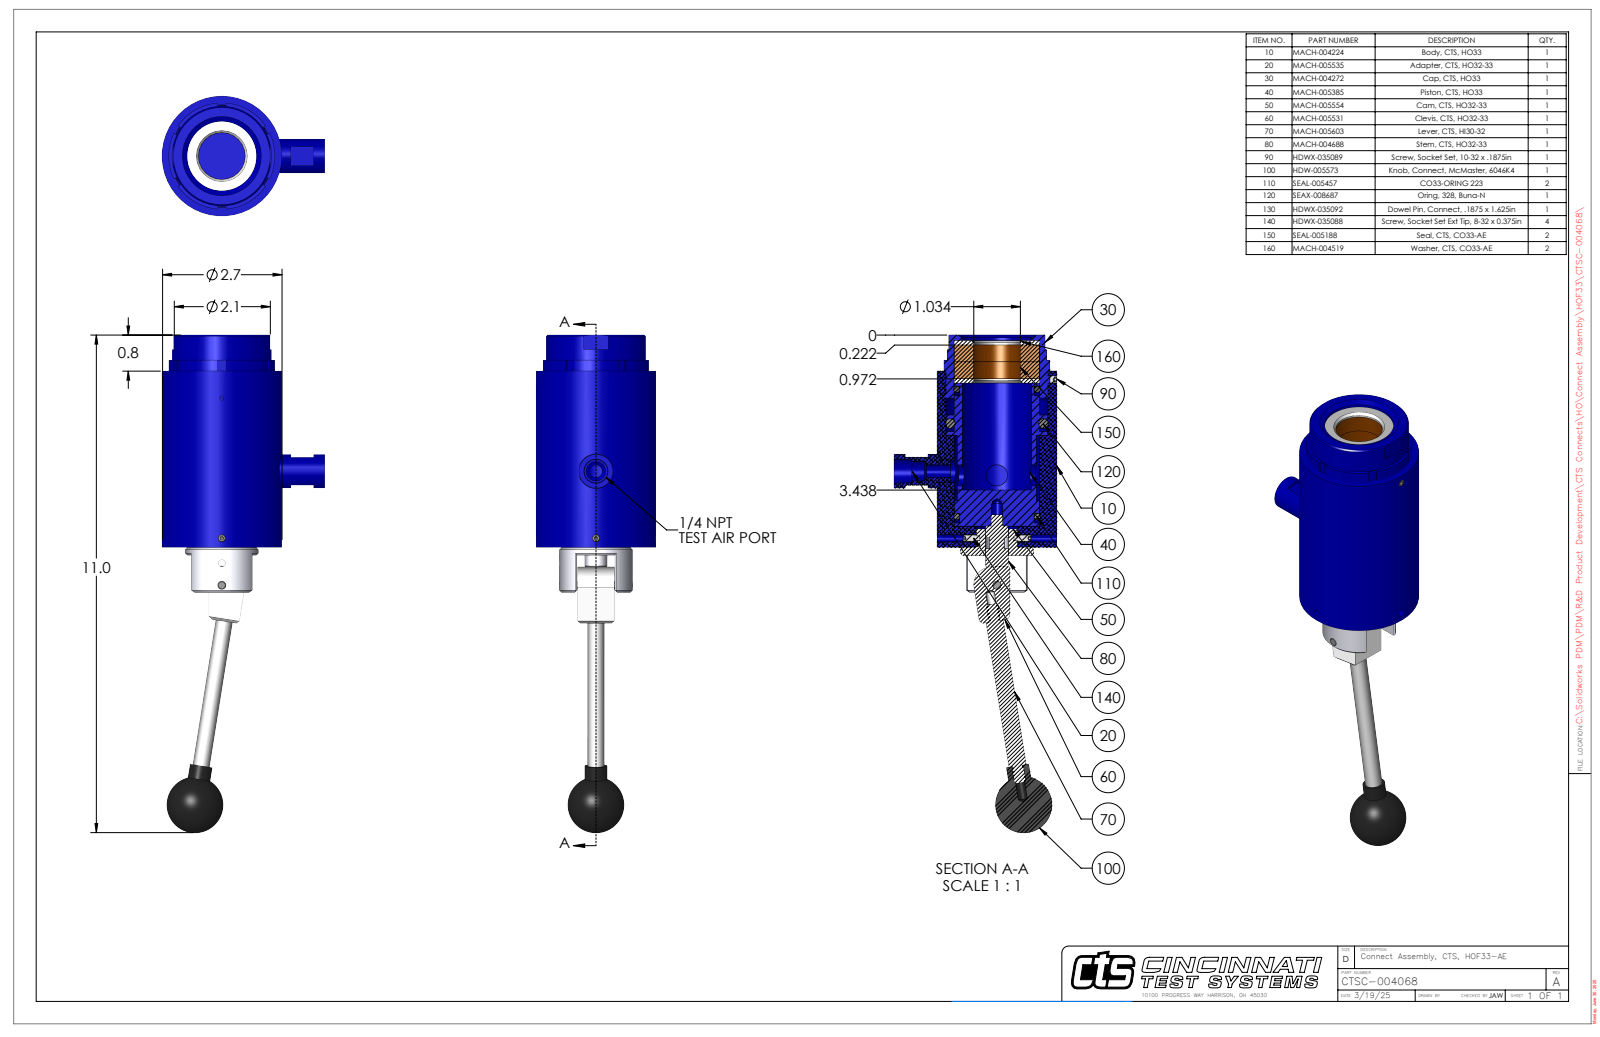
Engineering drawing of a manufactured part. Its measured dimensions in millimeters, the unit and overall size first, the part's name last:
Units: millimetres
Overall size (bounding box): 280.3 × 91.4 × 67.3
Round holes (diameter × count): ⌀5.1 ×3, ⌀4 ×2, ⌀11.9 ×2, ⌀2.4 ×1, ⌀4.8 ×1, ⌀4.8 ×1, ⌀6.4 ×1, ⌀7.1 ×1, ⌀11.1 ×1, ⌀12.7 ×1, ⌀13.1 ×1, ⌀13.5 ×1
Round bosses / shafts (diameter × count): ⌀19.1 ×2, ⌀12.7 ×2, ⌀4.2 ×2, ⌀2.8 ×2, ⌀67.3 ×1, ⌀59.5 ×1, ⌀55.9 ×1, ⌀47.9 ×1
Partial cylindrical surfaces — rounded edges, fillets, slot ends (radius × count): R9.8 ×1, R10.2 ×1, R28.7 ×1, R30.1 ×1
Main face-to-face distances: 21.4, 2.4, 19.1, 94.9, 113.9, 9.5, 9.5, 104.4, 11.9, 92.5
Hole centre spacings: 2.4, 12.4, 43.5, 49.4, 51.6, 54, 61.8, 92.9
Volume: 364 600 mm³ · Surface area: 90 060 mm²
Bodies: 15 solids, 546 faces (179 planar, 226 cylindrical, 141 other)
Part name (STEP PRODUCT): CTSC-004068
STEP written by: SolidWorks 2023 (AUTOMOTIVE_DESIGN)
